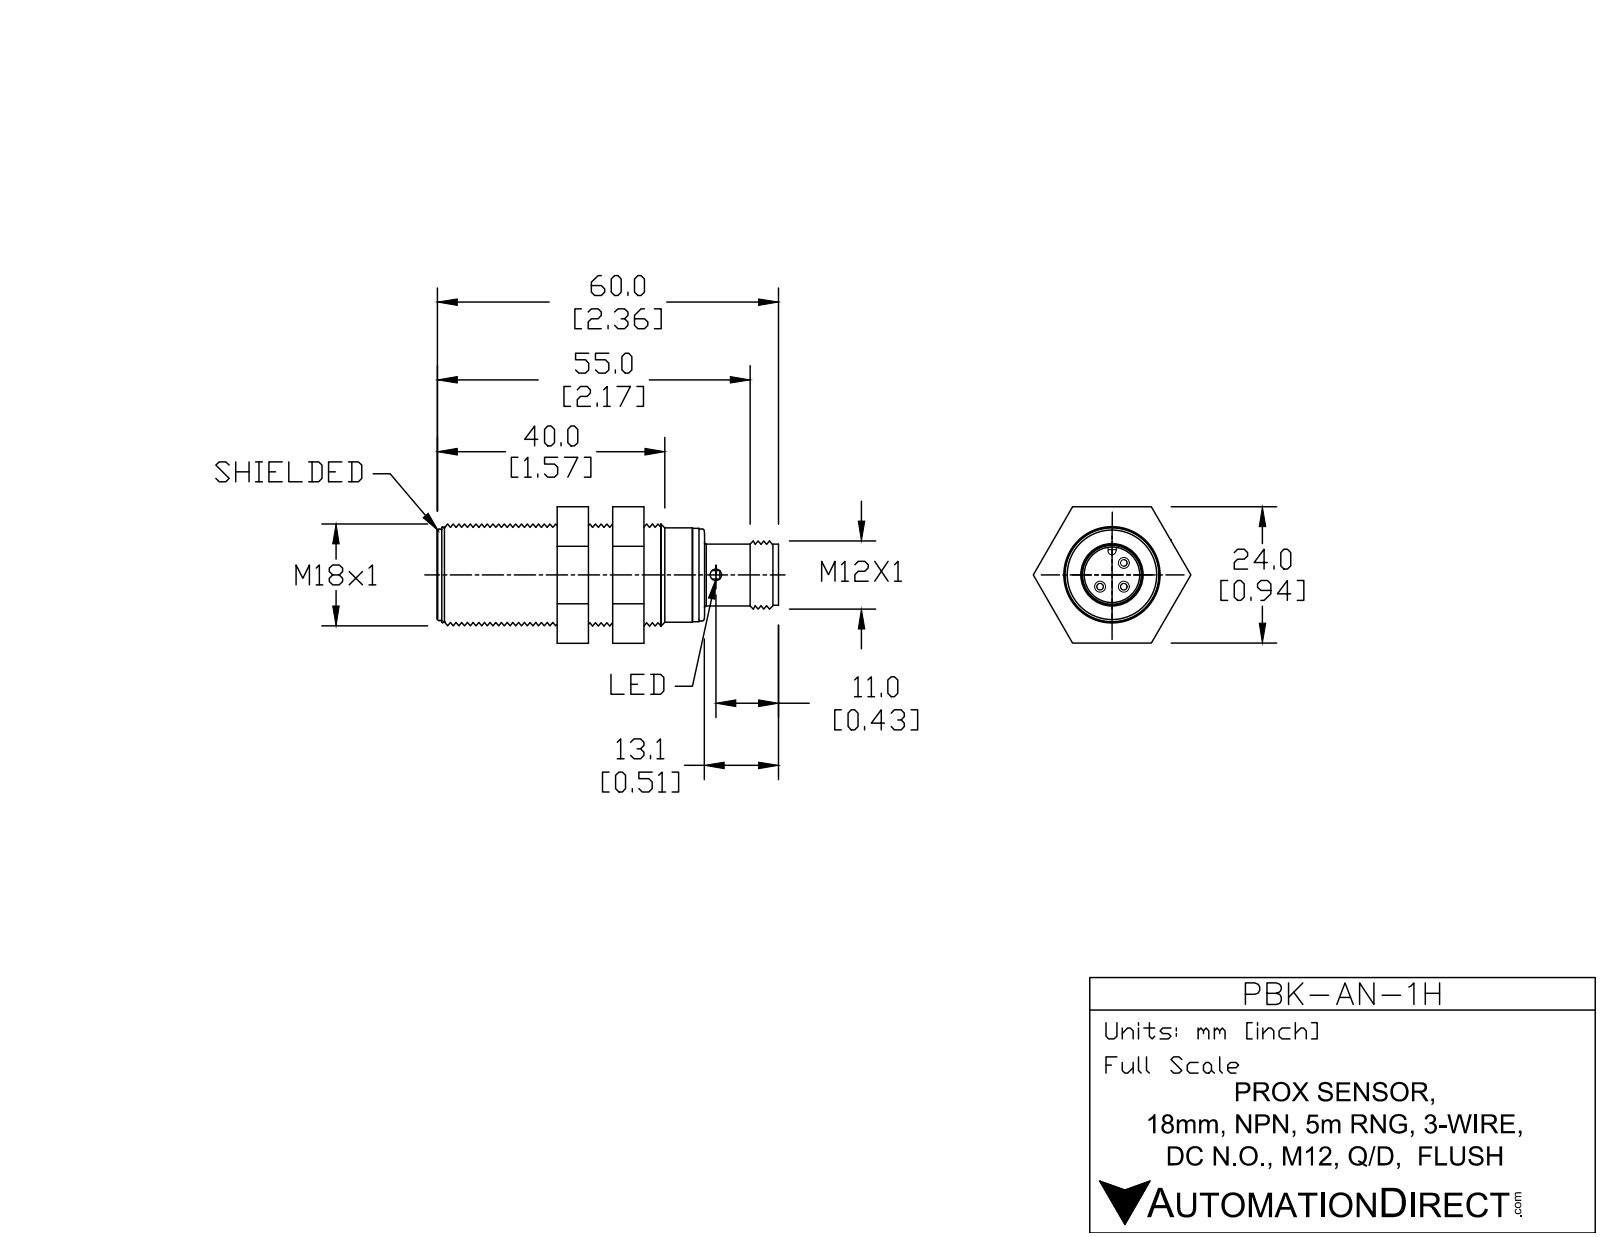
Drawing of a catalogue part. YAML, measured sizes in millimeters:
part_name: "PBK-AN-1H"
step_written_by: "SolidWorks 2017 (AUTOMOTIVE_DESIGN)"
units: millimeters
bodies: {solids: 3, faces: 131, planar: 28, cylindrical: 37, other: 66}
overall_size: [60, 27.7, 24]
volume: 14800
surface_area: 5957
round_holes:
  - {diameter: 2.5, count: 2}
  - {diameter: 8.3, count: 1}
  - {diameter: 16.1, count: 1}
  - {diameter: 16.9, count: 1}
round_bosses_or_shafts:
  - {diameter: 18, count: 1}
  - {diameter: 16.6, count: 1}
  - {diameter: 16.2, count: 1}
  - {diameter: 16, count: 1}
  - {diameter: 12, count: 1}
  - {diameter: 10.8, count: 1}
partial_cylinders:
  - {radius: 0.6, count: 1}
  - {radius: 4.7, count: 1}
face_to_face_distances: [4, 24, 29, 33, 8, 25, 14.8, 18.8, 22.8, 47.8]
